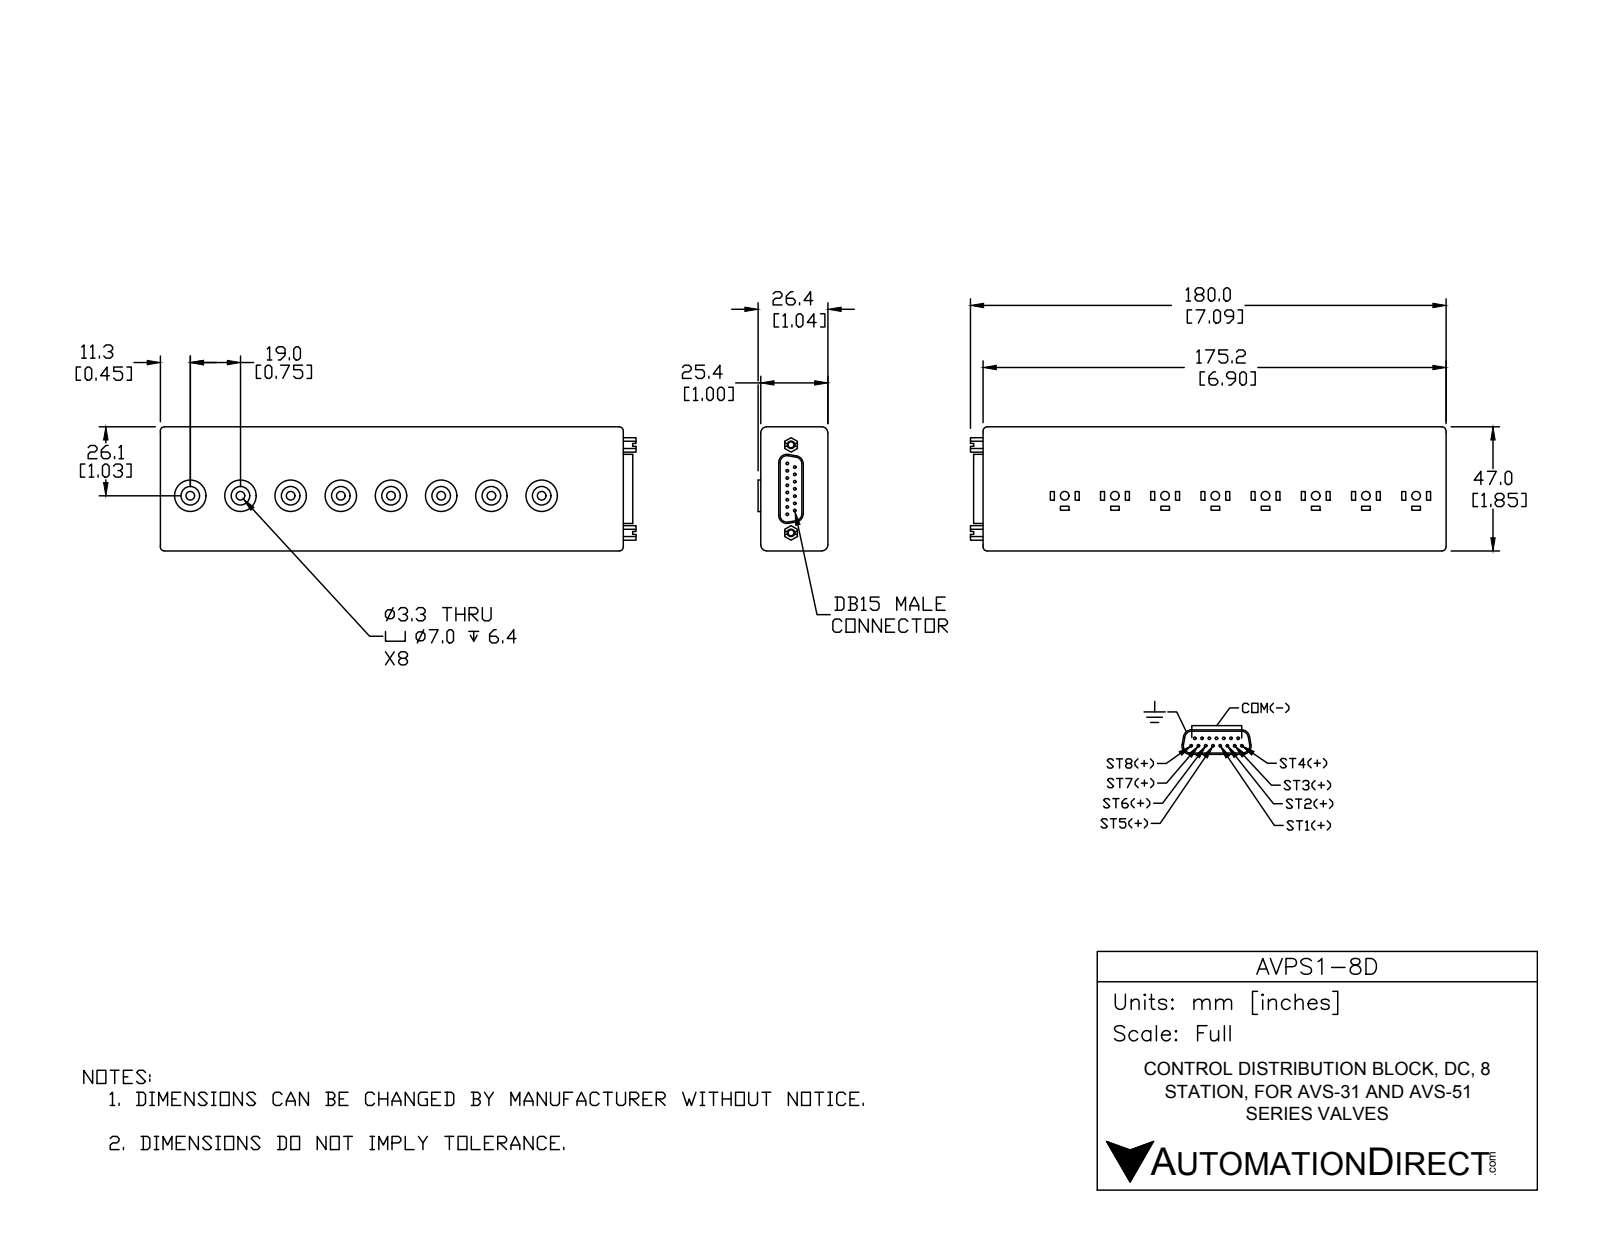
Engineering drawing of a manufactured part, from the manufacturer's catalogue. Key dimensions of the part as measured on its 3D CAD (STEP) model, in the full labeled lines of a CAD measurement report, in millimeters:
Part name (STEP PRODUCT): AVPS1-8D
STEP written by: SolidWorks 2016 (AUTOMOTIVE_DESIGN)
Units: millimetres
Bodies: 1 solid, 311 faces (195 planar, 104 cylindrical, 12 other)
Overall size (bounding box): 180 × 47 × 26.4
Volume: 204 800 mm³ · Surface area: 32 390 mm²
Round holes (diameter × count): ⌀3.3 ×8, ⌀7 ×8, ⌀2.3 ×2
Round bosses / shafts (diameter × count): ⌀1 ×15, ⌀11.9 ×8
Partial cylindrical surfaces — rounded edges, fillets, slot ends (radius × count): R1.6 ×8, R2.3 ×4, R2.6 ×4, R3.1 ×4
Main face-to-face distances: 25.4, 47, 175.2, 1, 26.4, 6.4, 20.1, 1.5, 19, 5.3
Hole centre spacings: 19, 38, 57, 76, 95, 114, 33.3, 133
